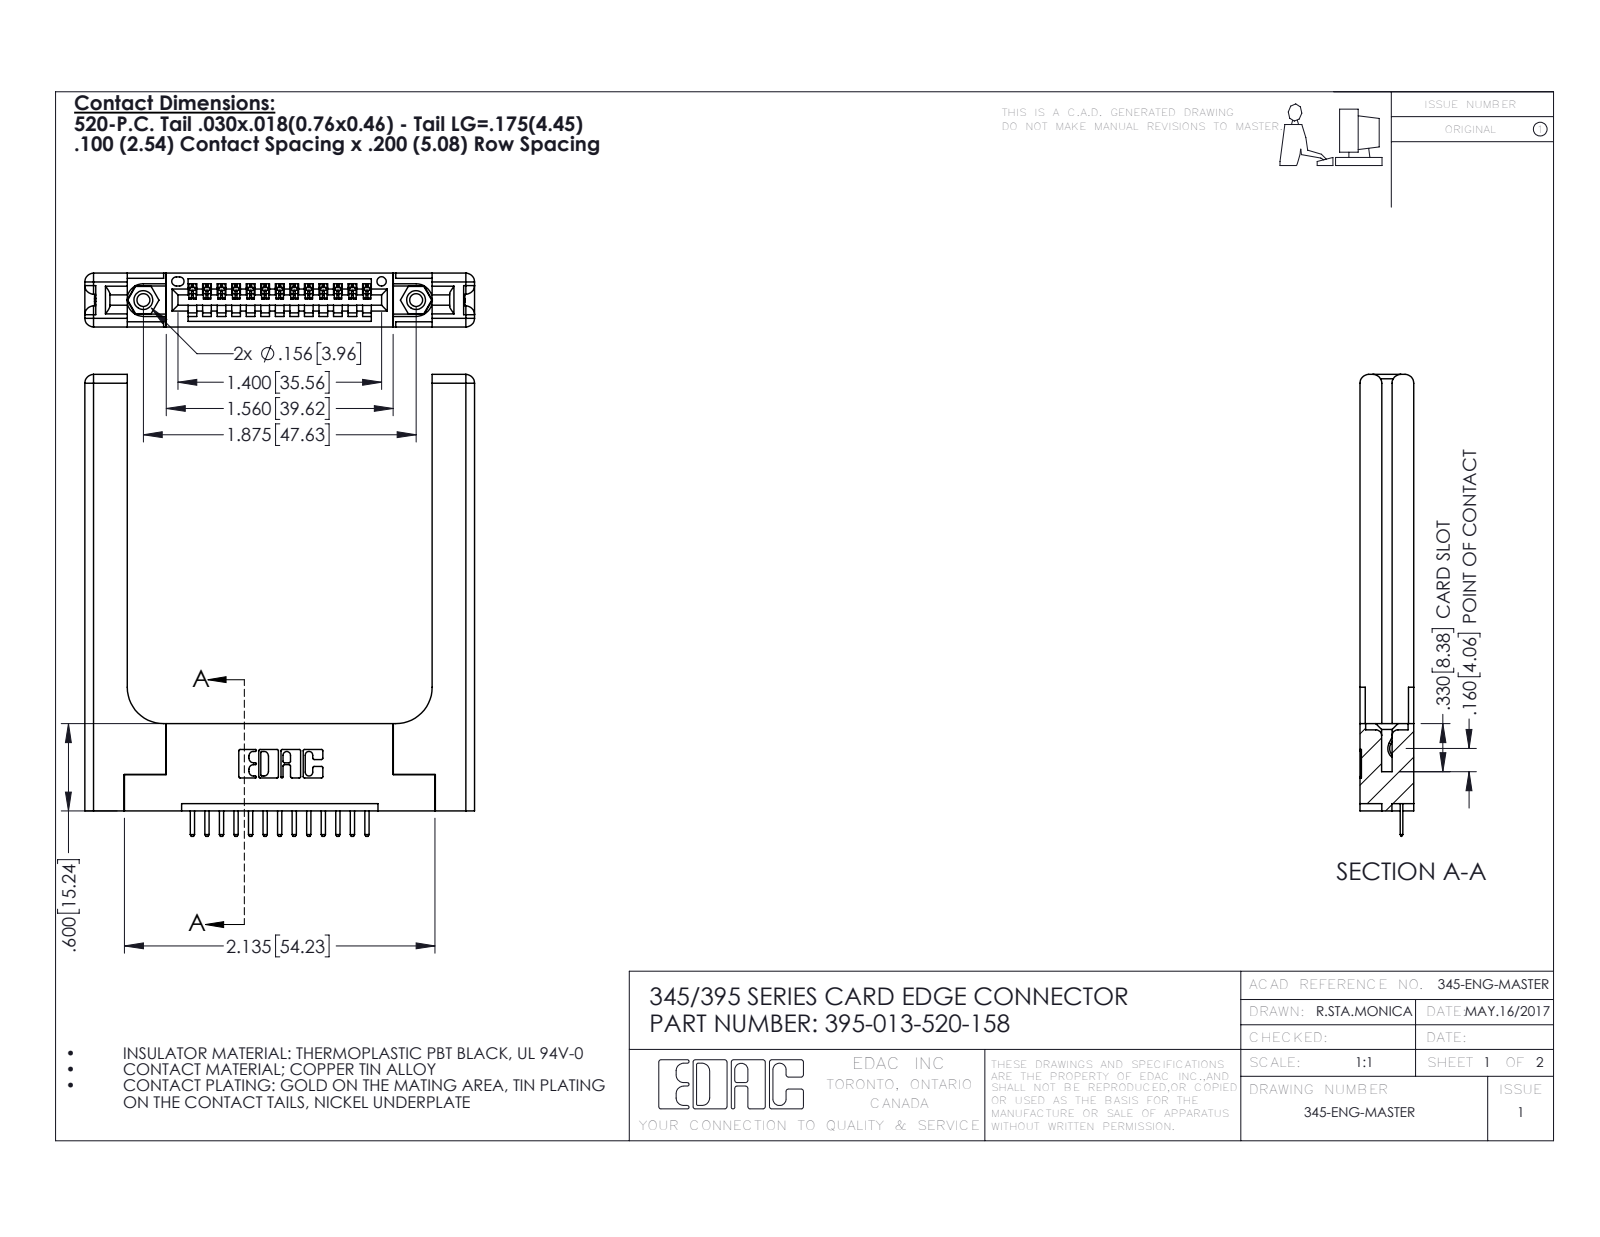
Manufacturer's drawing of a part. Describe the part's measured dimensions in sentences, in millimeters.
The part is named "345 Part_Flush Mounting Lugs - 0.156 Dia-TH; 345-292-001_345-293-120; 345-220-058_345-220-058; 395-013-520-158 (+1 more)". Its 3-D file was written by "SolidWorks 2016 (CONFIG_CONTROL_DESIGN)". It is 18 solids with 1188 faces: 774 planar, 354 cylindrical and 60 other. Overall it measures 80.6 by 68 by 9.4 millimeters. Its volume is 14 700 cubic millimeters and its surface area 13 010 square millimeters. Round holes: 2 of diameter 2.3, 2 of diameter 3.2, 2 of diameter 4, 1 of diameter 1.6. Round bosses or shafts: 2 of diameter 3.9. Partial cylindrical surfaces (rounded edges, fillets, slot ends): 28 of radius 0.3, 26 of radius 0.2, 22 of radius 0.3, 16 of radius 1.5, 6 of radius 0.2, 6 of radius 0.8, 3 of radius 0.7, 2 of radius 0.8. The main face-to-face distances are 9.4, 1.8, 3.8, 2, 3.8, 5.6, 7.6, 5.1, 53.2, 1.8. The hole center spacings are 6.9, 41.7, 47.6.
